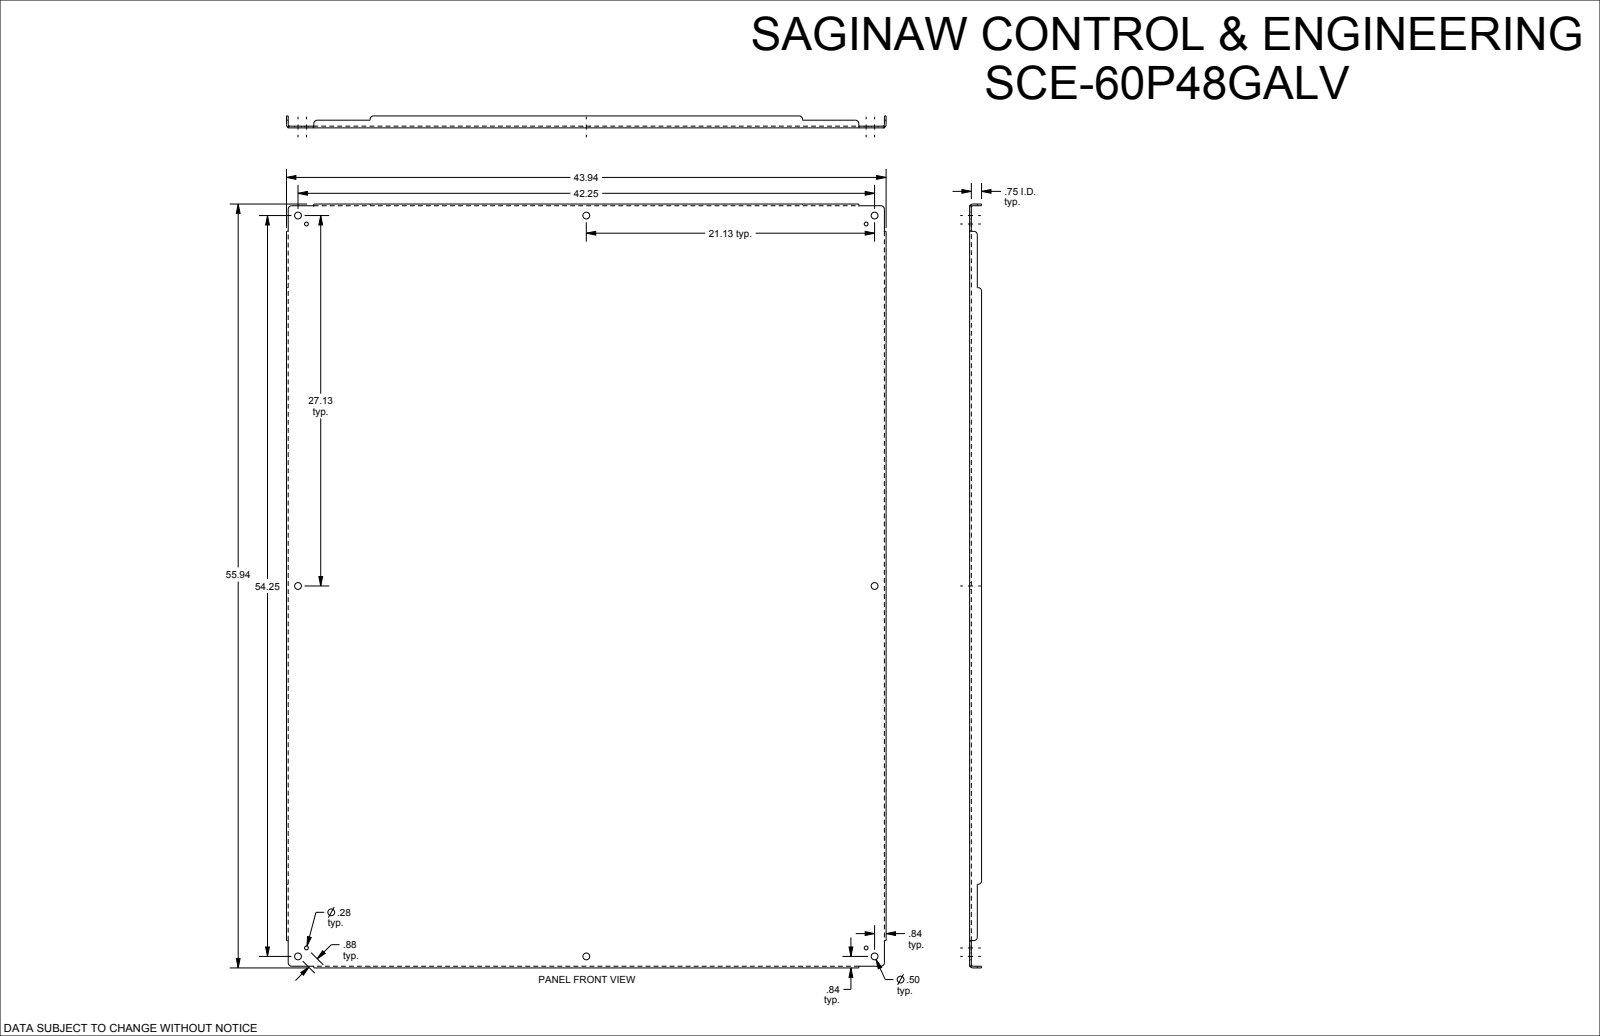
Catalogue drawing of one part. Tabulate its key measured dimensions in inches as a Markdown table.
| quantity | value |
| --- | --- |
| part name | SCE-60P48GALV |
| STEP written by | SolidWorks 2019 (CONFIG_CONTROL_DESIGN) |
| units | inches |
| bodies | 1 solid, 110 faces (46 planar, 40 cylindrical, 24 other) |
| overall size | 55.938 × 43.938 × 0.875 |
| volume | 320.9 in³ |
| surface area | 5 162 in² |
| round holes (diameter × count) | 0.5 × 8, 0.281 × 4 |
| partial cylindrical surfaces (radius × count) | 0.25 × 12, 0.112 × 4, 0.237 × 4 |
| main face-to-face distances | 0.125, 0.125, 43.813, 55.813, 43.687, 43.938, 55.687, 55.938, 0.75, 0.875 |
| hole center spacings | 0.875, 20.516, 21.125, 26.513, 27.125, 34.38, 41.636, 49.353 |
